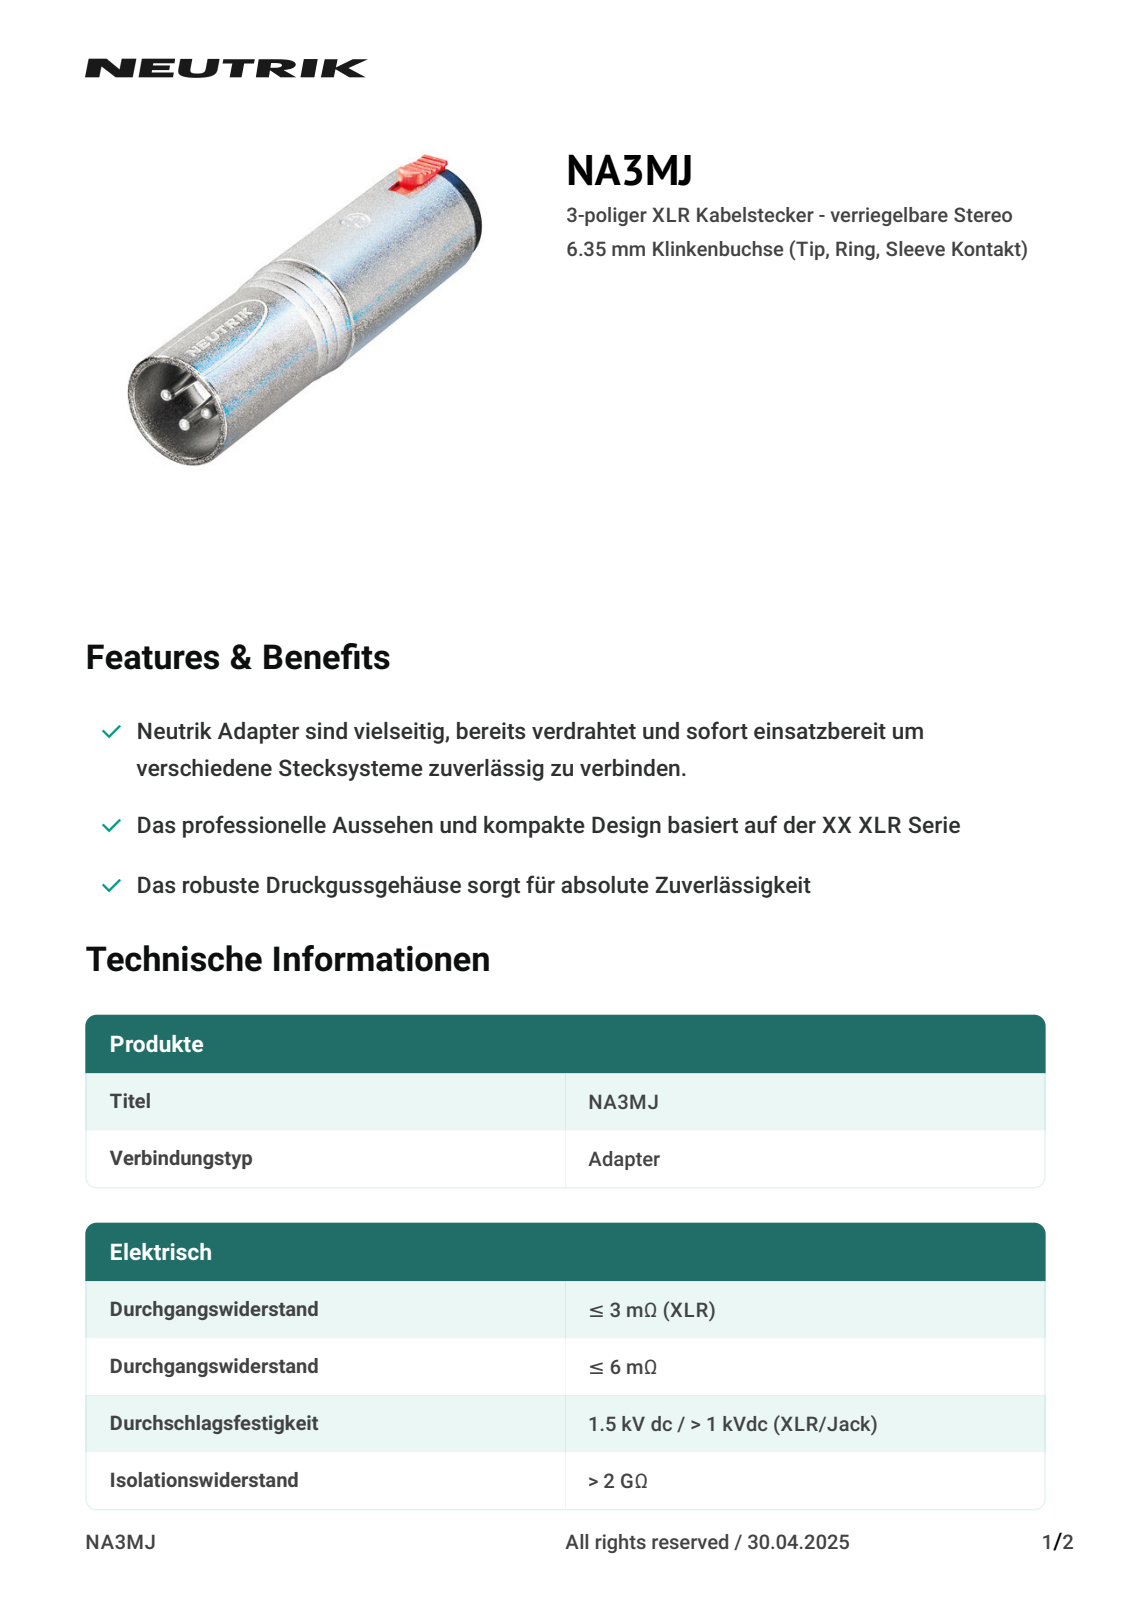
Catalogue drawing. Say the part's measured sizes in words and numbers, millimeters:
The part is named "NA3MJ". Its 3-D file was written by "CREO PARAMETRIC BY PTC INC, 2018360 (CONFIG_CONTROL_DESIGN)". It is 1 solid with 726 faces: 483 planar, 91 cylindrical and 152 other. Overall it measures 77.35 by 21.93 by 20.97 millimeters. Its volume is 20 183 cubic millimeters and its surface area 6 808 square millimeters. Round holes: 3 of diameter 2.41, 1 of diameter 5, 1 of diameter 5.1, 1 of diameter 6.5, 1 of diameter 13. Round bosses or shafts: 3 of diameter 2.38, 1 of diameter 20, 1 of diameter 19, 1 of diameter 17.95, 1 of diameter 12.9, 1 of diameter 5. Partial cylindrical surfaces (rounded edges, fillets, slot ends): 9 of radius 0.2, 9 of radius 0.5, 1 of radius 0.27, 1 of radius 0.34, 1 of radius 0.69, 1 of radius 0.86, 1 of radius 1, 1 of radius 1.25. The main face-to-face distances are 62.65, 3.3, 59.35, 20.85, 38.5, 41.8, 20.7, 38.65, 41.95, 0.6. The hole center spacings are 4.05, 5.66, 3.95, 8.1.
